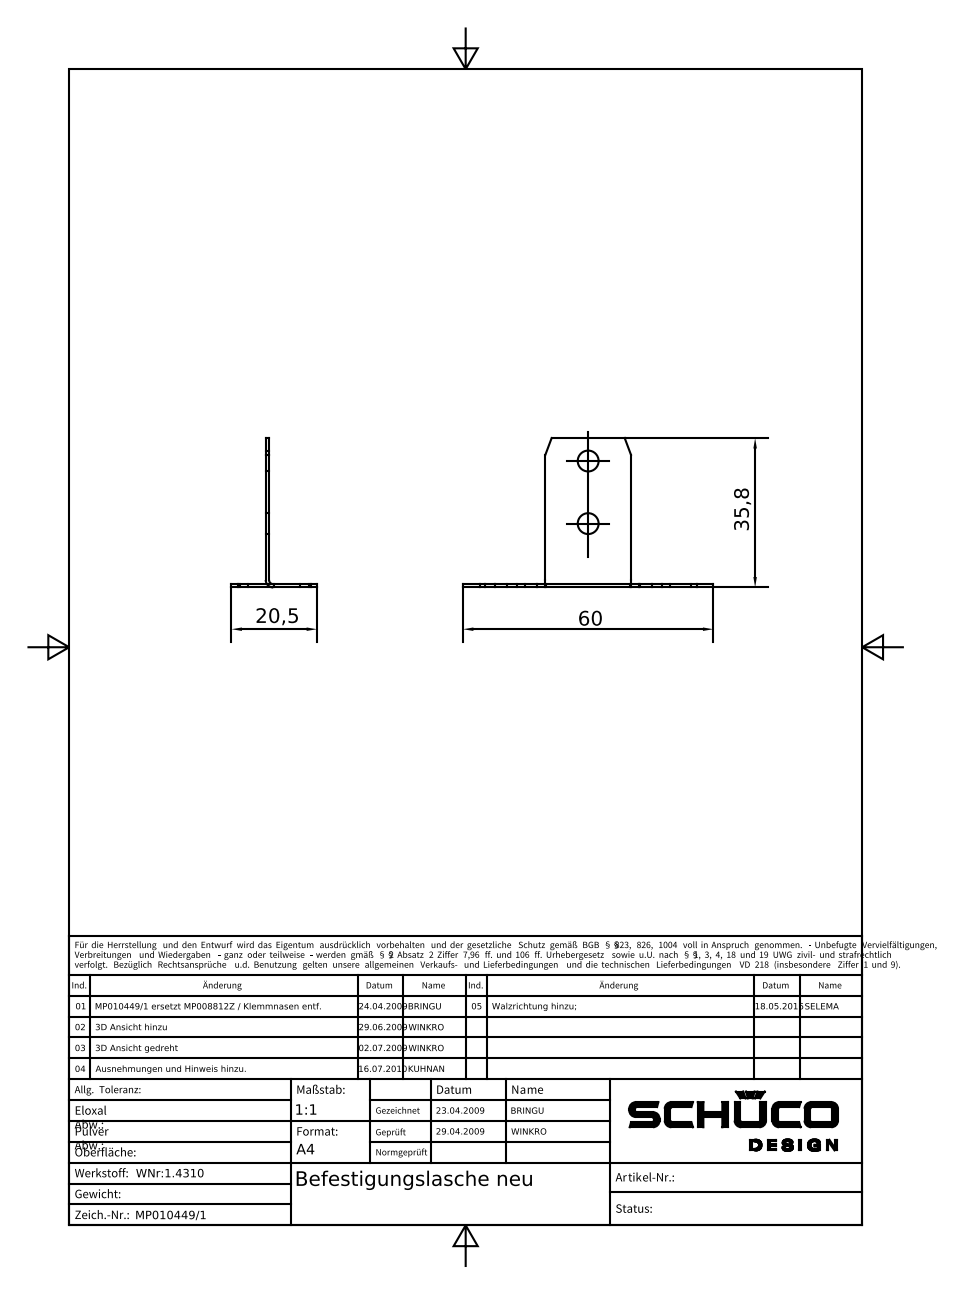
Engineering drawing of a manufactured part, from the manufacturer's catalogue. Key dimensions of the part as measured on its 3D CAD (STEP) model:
Part name (STEP PRODUCT): MP010449
STEP written by: Autodesk Inventor 2024 (AUTOMOTIVE_DESIGN)
Units: millimetres
Bodies: 1 solid, 50 faces (46 planar, 4 cylindrical, 0 other)
Overall size (bounding box): 60 × 35.8 × 20.5
Volume: 1 258 mm³ · Surface area: 3 439 mm²
Round holes (diameter × count): ⌀5 ×2
Partial cylindrical surfaces — rounded edges, fillets, slot ends (radius × count): R1 ×1, R1.8 ×1
Main face-to-face distances: 0.8, 2, 20.5, 16.5, 11.5, 12.3, 4, 19.75, 40.25, 14.5
Hole centre spacings: 15
